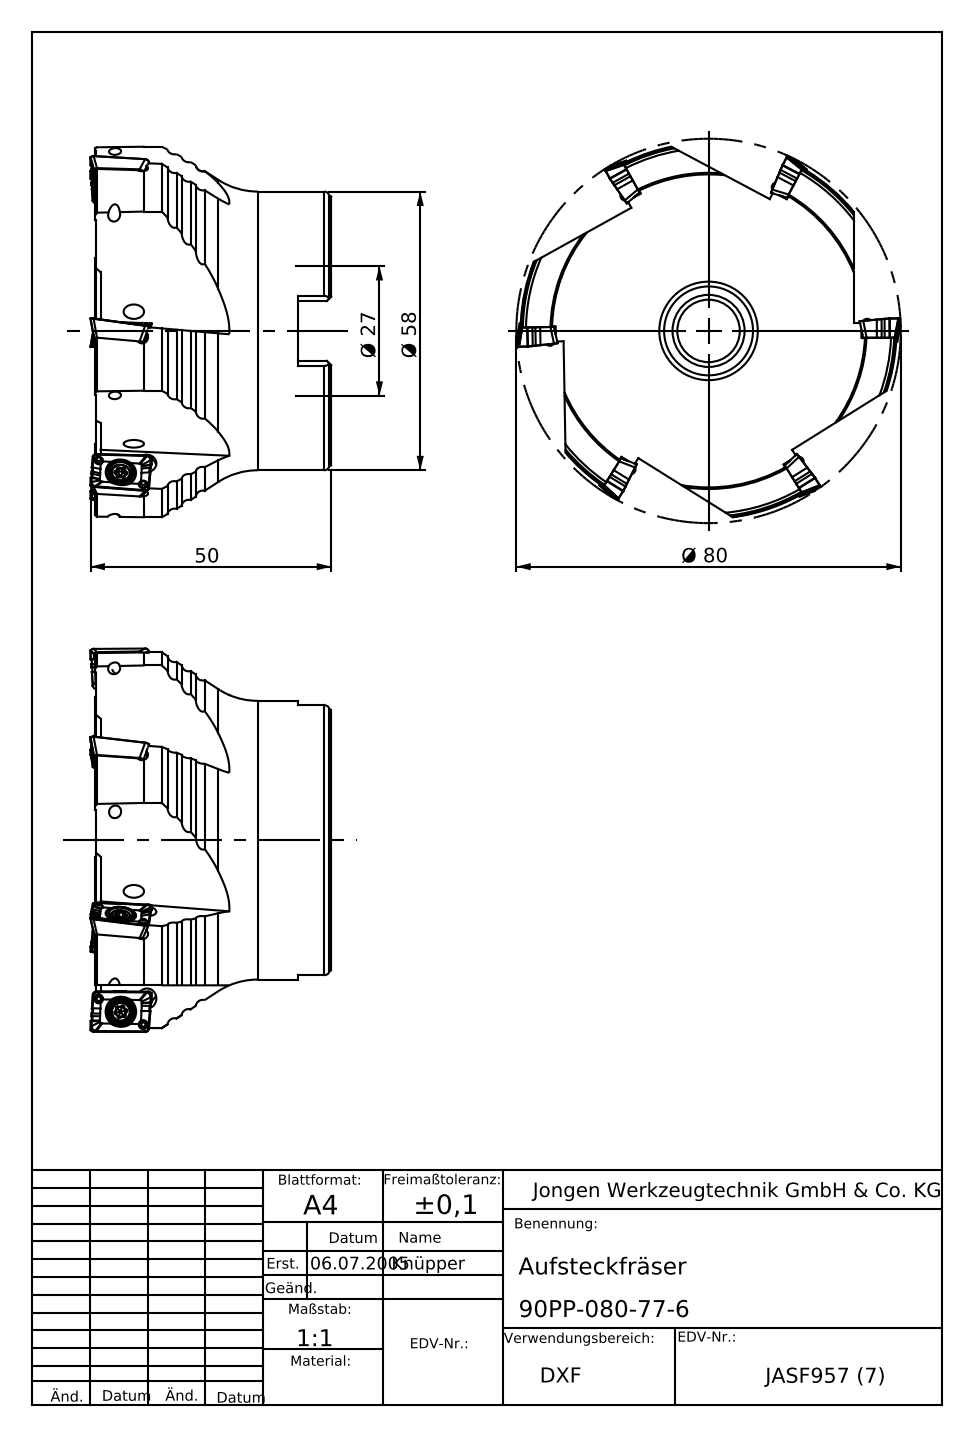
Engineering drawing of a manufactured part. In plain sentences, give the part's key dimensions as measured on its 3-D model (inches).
The part is named "90PP-080-77-6". Its 3-D file was written by "SolidWorks 2015 (AUTOMOTIVE_DESIGN)". It is 1 solid with 178 faces: 53 planar, 25 cylindrical and 100 other. Overall it measures 3.15 by 3.15 by 1.974 inches. Its volume is 8.899 cubic inches and its surface area 38.57 square inches. Round holes: 6 of diameter 0.118, 1 of diameter 0.512, 1 of diameter 0.728, 1 of diameter 1.063, 1 of diameter 1.069, 1 of diameter 1.075, 1 of diameter 2.476. Round bosses or shafts: 1 of diameter 2.283. Partial cylindrical surfaces (rounded edges, fillets, slot ends): 6 of radius 0.079, 1 of radius 1.539. The main face-to-face distances are 1.892, 0.982, 0.909, 0.278, 0.705, 1.614, 0.491, 1.341, 1.063, 0.358.
